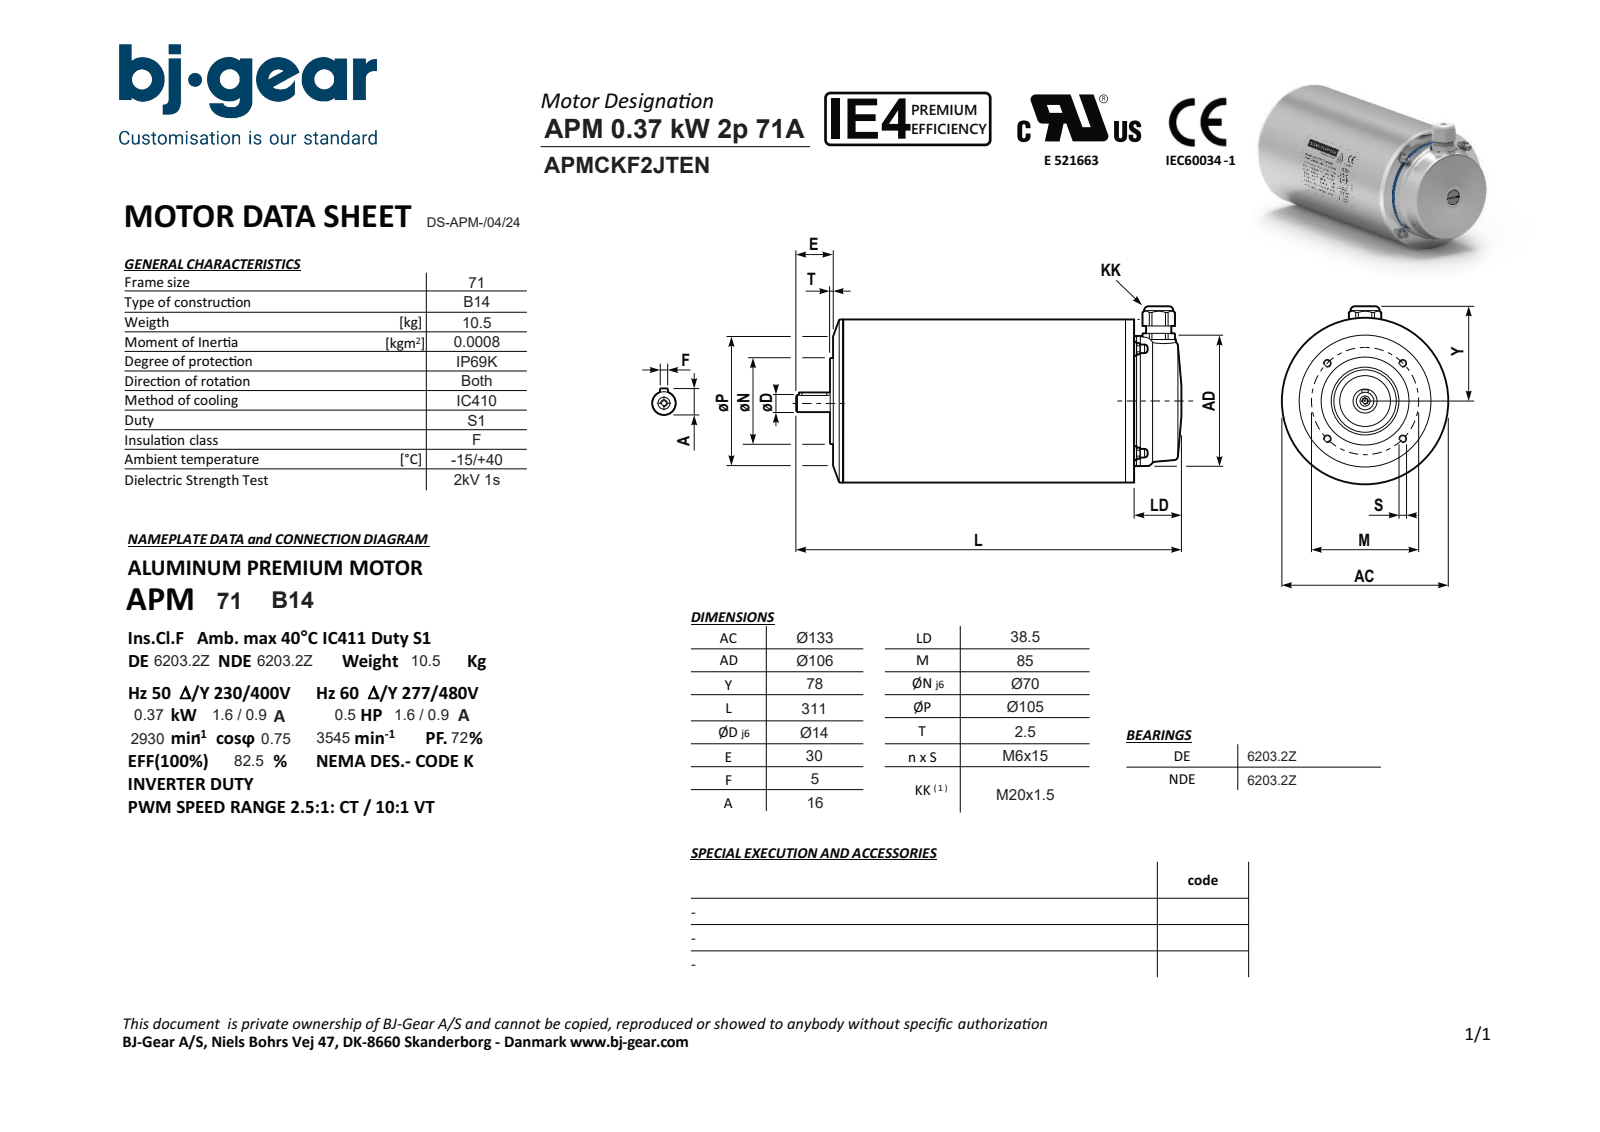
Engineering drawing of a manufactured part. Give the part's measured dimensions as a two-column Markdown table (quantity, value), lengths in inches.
| quantity | value |
| --- | --- |
| part name | APMCKF2JTENN4KCR2-N---NNN |
| STEP written by | Solid Edge (AUTOMOTIVE_DESIGN) |
| units | inches |
| bodies | 1 solid, 156 faces (71 planar, 50 cylindrical, 35 other) |
| overall size | 12.244 × 5.642 × 5.22 |
| volume | 222.1 in³ |
| surface area | 225 in² |
| round holes (diameter × count) | 0.194 × 4, 0.163 × 1, 0.209 × 1, 0.63 × 1, 1.102 × 1, 2.047 × 1 |
| round bosses / shafts (diameter × count) | 0.453 × 4, 0.276 × 4, 5.22 × 1, 5.22 × 1, 4.173 × 1, 2.756 × 1, 0.933 × 1, 0.811 × 1 |
| partial cylindrical surfaces (radius × count) | 0.098 × 2, 0.52 × 1 |
| main face-to-face distances | 9.547, 9.331, 0.217, 0.315, 0.098, 9.646, 11.161, 1.516, 10.846, 11.063 |
| hole center spacings | 1.673, 2.366, 3.346 |
